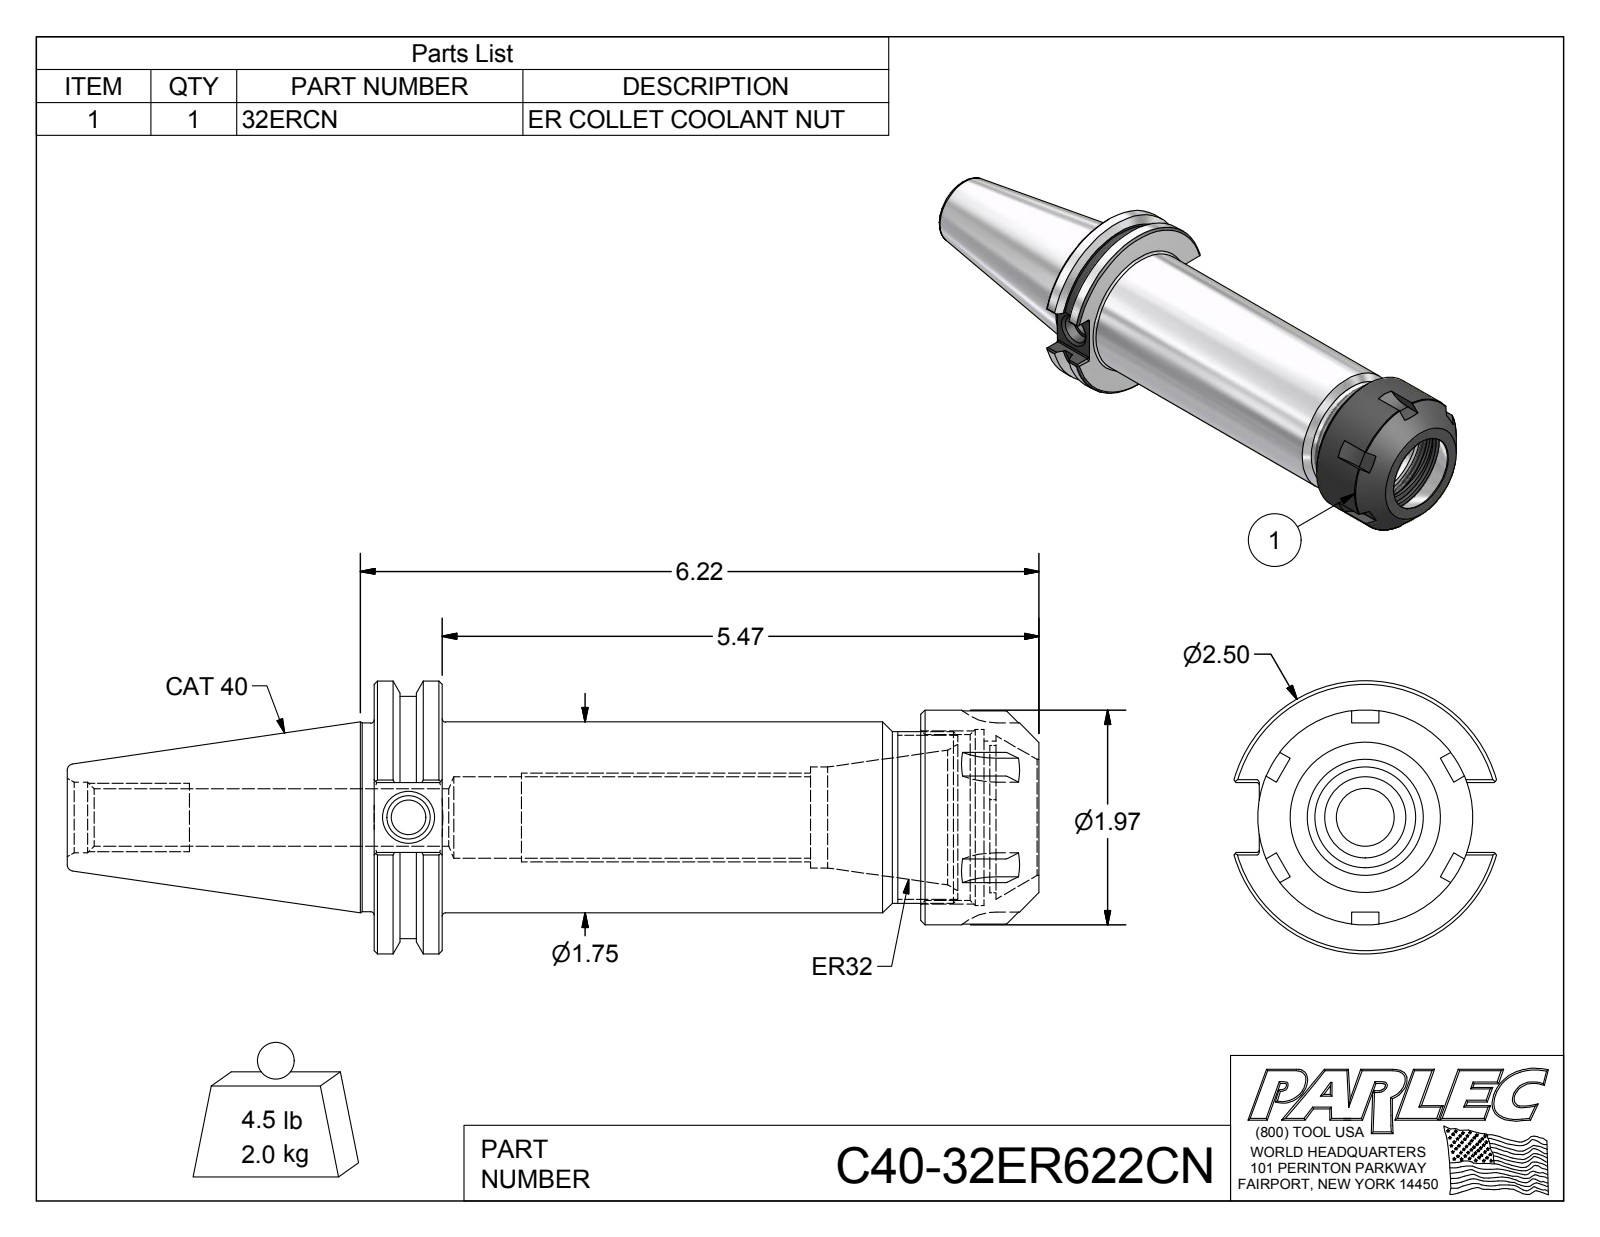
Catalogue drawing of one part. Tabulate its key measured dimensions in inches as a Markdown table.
| quantity | value |
| --- | --- |
| part name | C40-32ER622CN; C40-32ER6-1; 32ERCN |
| STEP written by | Autodesk Inventor 2012 (AUTOMOTIVE_DESIGN) |
| units | inches |
| bodies | 2 solids, 127 faces (55 planar, 39 cylindrical, 33 other) |
| overall size | 8.908 × 2.5 × 2.403 |
| volume | 15.74 in³ |
| surface area | 83.54 in² |
| round holes (diameter × count) | 0.315 × 1, 0.399 × 1, 0.527 × 1, 0.648 × 1, 0.745 × 1, 0.925 × 1, 1.063 × 1, 1.299 × 1, 1.522 × 1, 1.614 × 1 |
| round bosses / shafts (diameter × count) | 2.5 × 1, 2.219 × 1, 1.969 × 1, 1.75 × 1, 1.73 × 1, 1.575 × 1 |
| partial cylindrical surfaces (radius × count) | 0.02 × 12, 0.5 × 6, 0.689 × 1 |
| main face-to-face distances | 0.625, 5.012, 4.387, 5.591, 4.966, 0.579, 6.095, 5.47, 1.083, 0.504 |
| hole center spacings | 0.059 |
